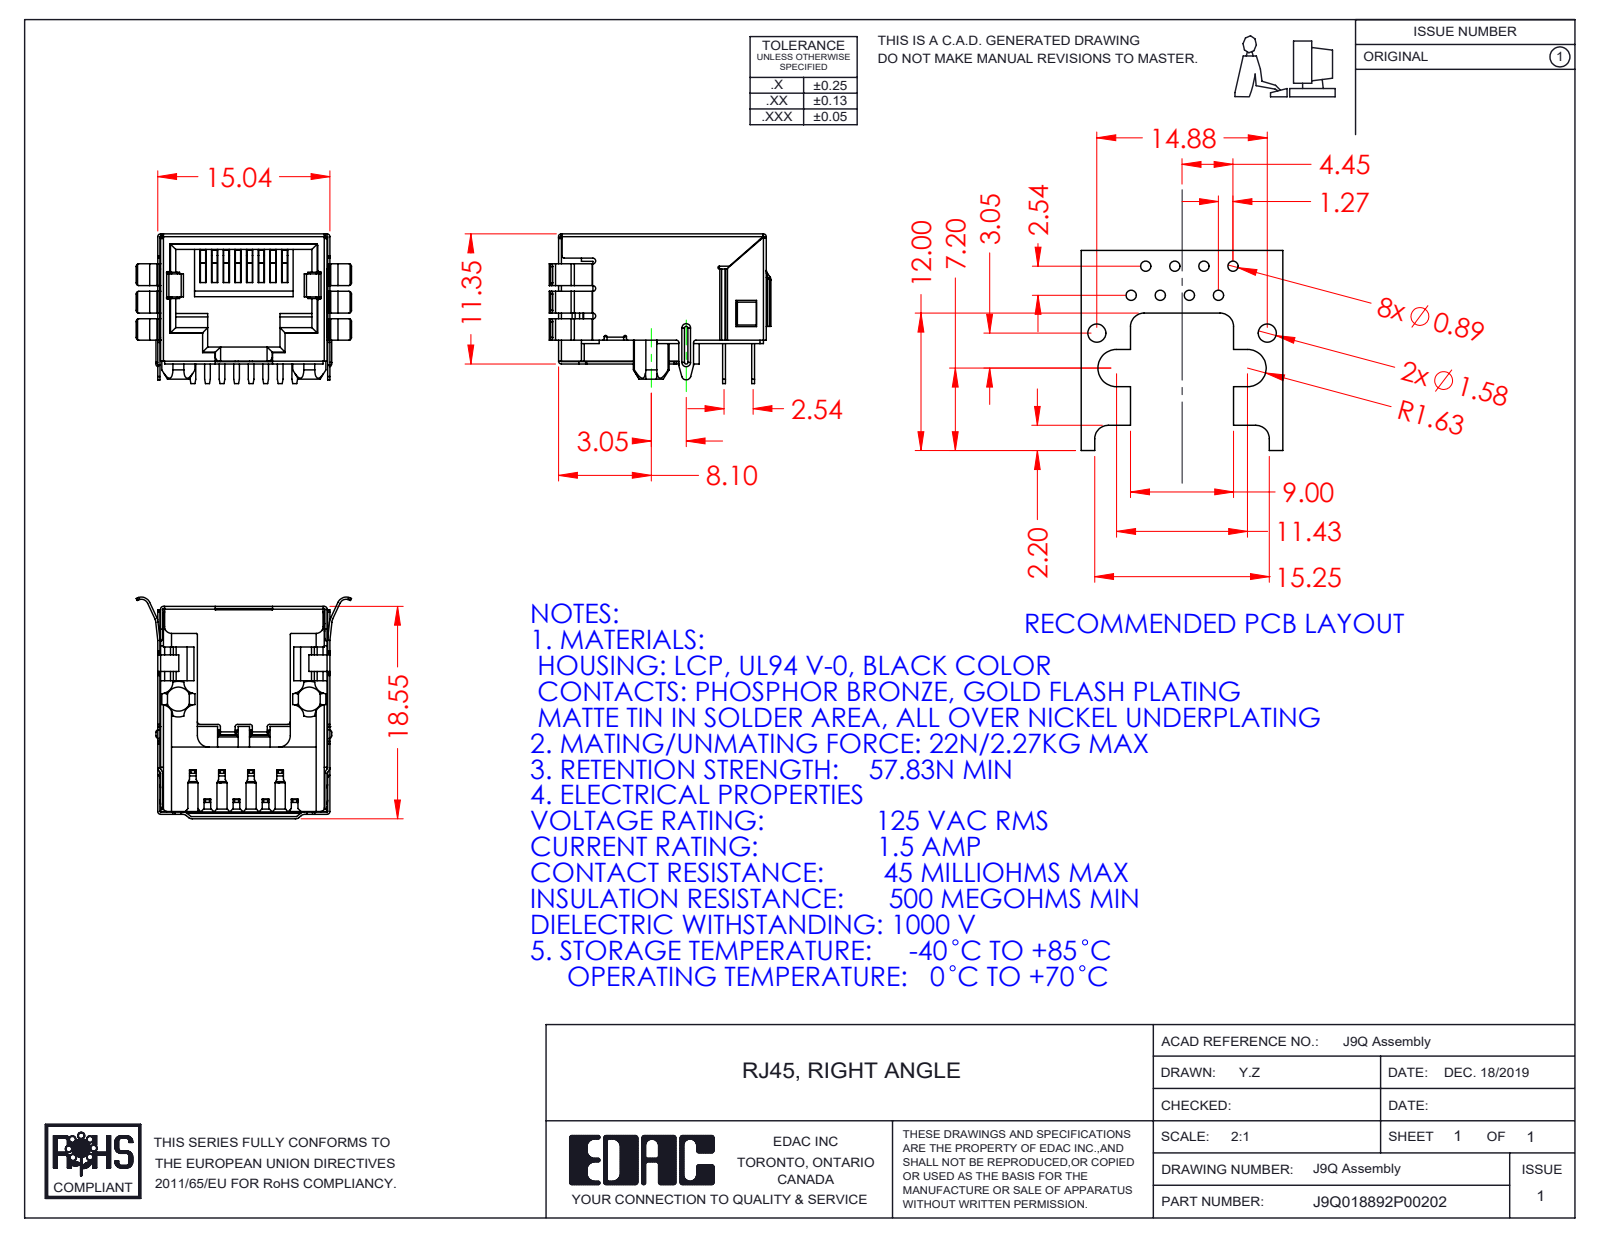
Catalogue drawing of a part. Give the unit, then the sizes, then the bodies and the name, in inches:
Units: inches
Overall size (bounding box): 0.762 × 0.741 × 0.515
Partial cylindrical surfaces — rounded edges, fillets, slot ends (radius × count): R0.004 ×43, R0.008 ×35, R0.01 ×34, R0.006 ×24, R0.02 ×19, R0.012 ×14, R0.024 ×8, R0.041 ×8
Main face-to-face distances: 0.574, 0.572, 0.584, 0.565, 0.582, 0.02, 0.439, 0.563, 0.576, 0.592
Volume: 0.073 in³ · Surface area: 7.468 in²
Bodies: 11 solids, 1339 faces (949 planar, 369 cylindrical, 21 other)
Part name (STEP PRODUCT): J9Q018892P00202; 9Q Contacts; 9Q Shield; 9Q Contact Lock (+1 more)
STEP written by: SolidWorks 2016 (CONFIG_CONTROL_DESIGN)
